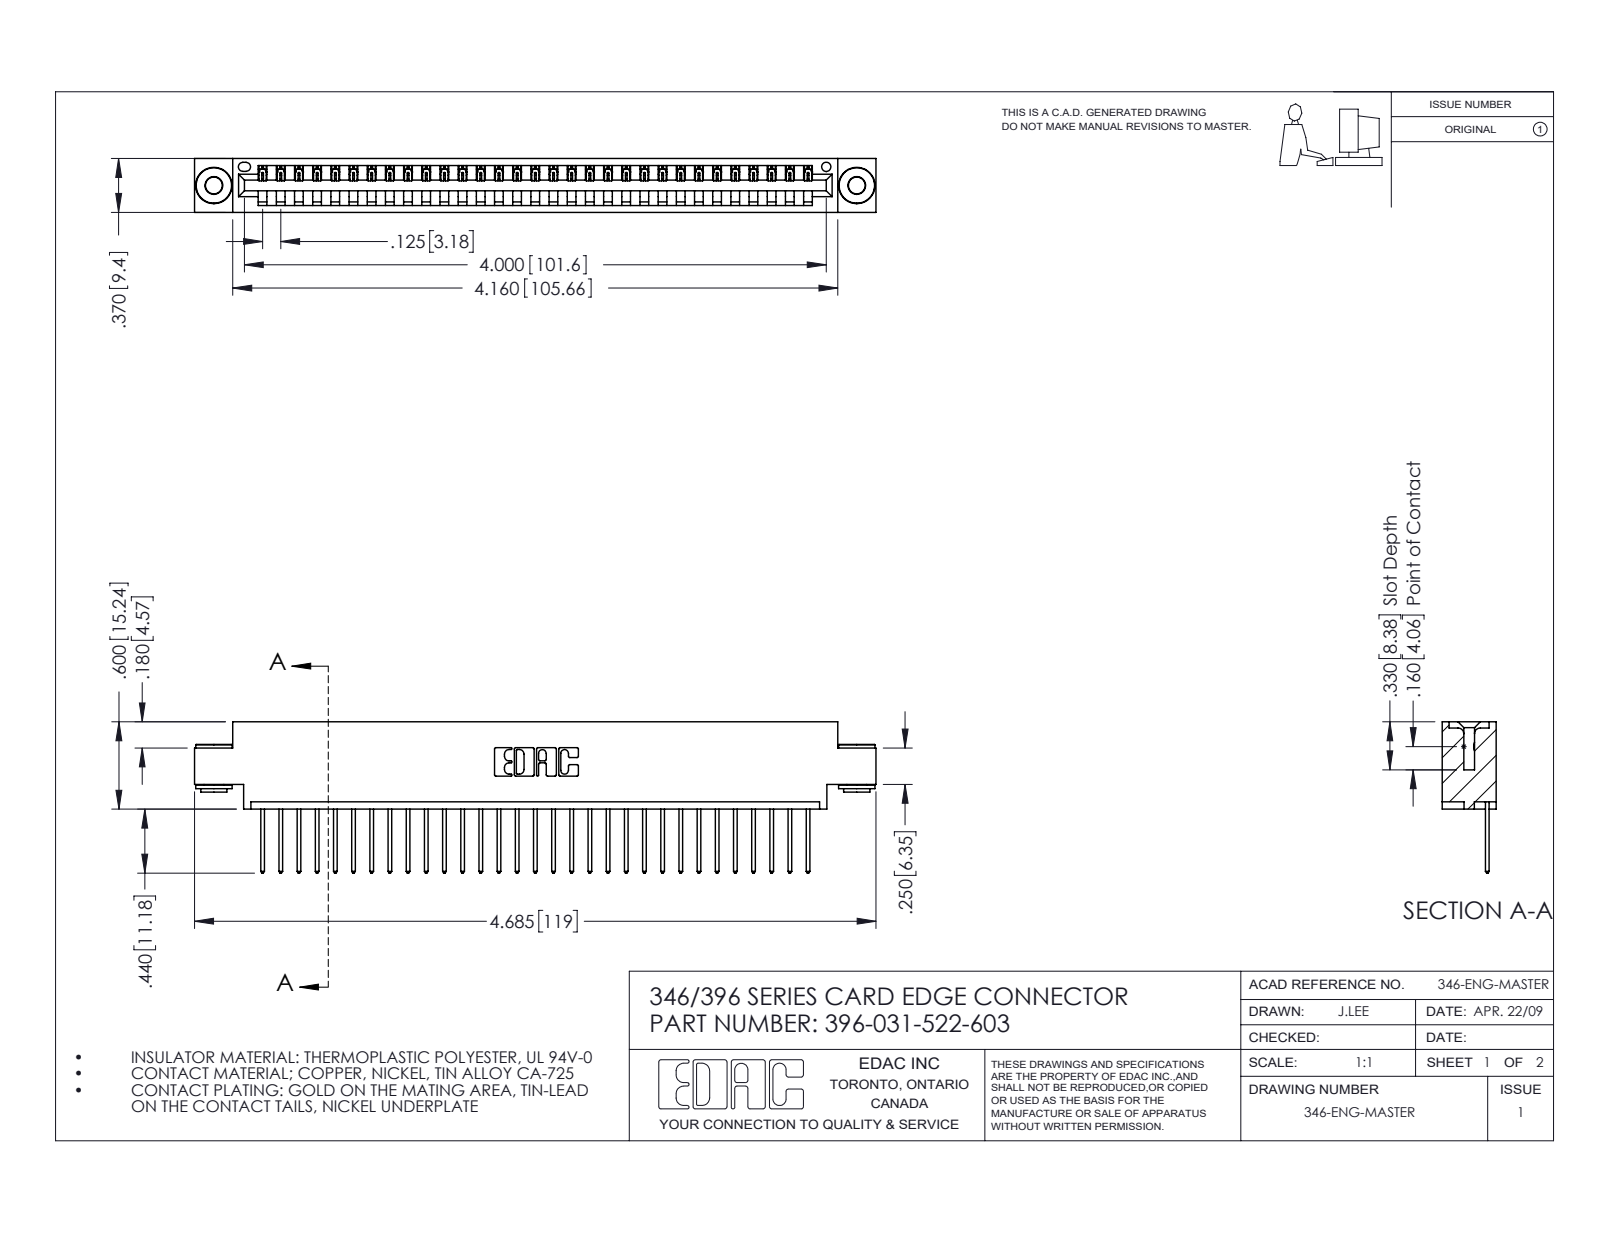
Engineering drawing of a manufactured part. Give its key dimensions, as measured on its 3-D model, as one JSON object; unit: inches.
{"part_name": "396-031-522-603; 346 Part_0.170 Offset - 0.156 Dia-TH; 345-292-001_345-293-122; 345-250-002_345-250-002-102", "step_written_by": "SolidWorks 2016 (CONFIG_CONTROL_DESIGN)", "units": "inches", "bodies": {"solids": 34, "faces": 1962, "planar": 1330, "cylindrical": 624, "other": 8}, "overall_size": [4.685, 1.04, 0.37], "volume_in3": 0.682, "surface_area_in2": 22.25, "round_holes": [[0.116, 2], [0.156, 2], [0.064, 1]], "round_bosses_or_shafts": [[0.25, 2], [0.18, 2], [0.136, 2]], "partial_cylinders_radius": [[0.006, 62], [0.01, 62], [0.01, 22], [0.007, 6], [0.031, 6], [0.026, 3], [0.031, 2], [0.04, 2]], "face_to_face_distances": [0.048, 0.322, 0.37, 0.25, 0.025, 0.072, 0.298, 0.148, 0.222, 0.1], "hole_center_spacings": [0.246, 4.212, 4.42]}
